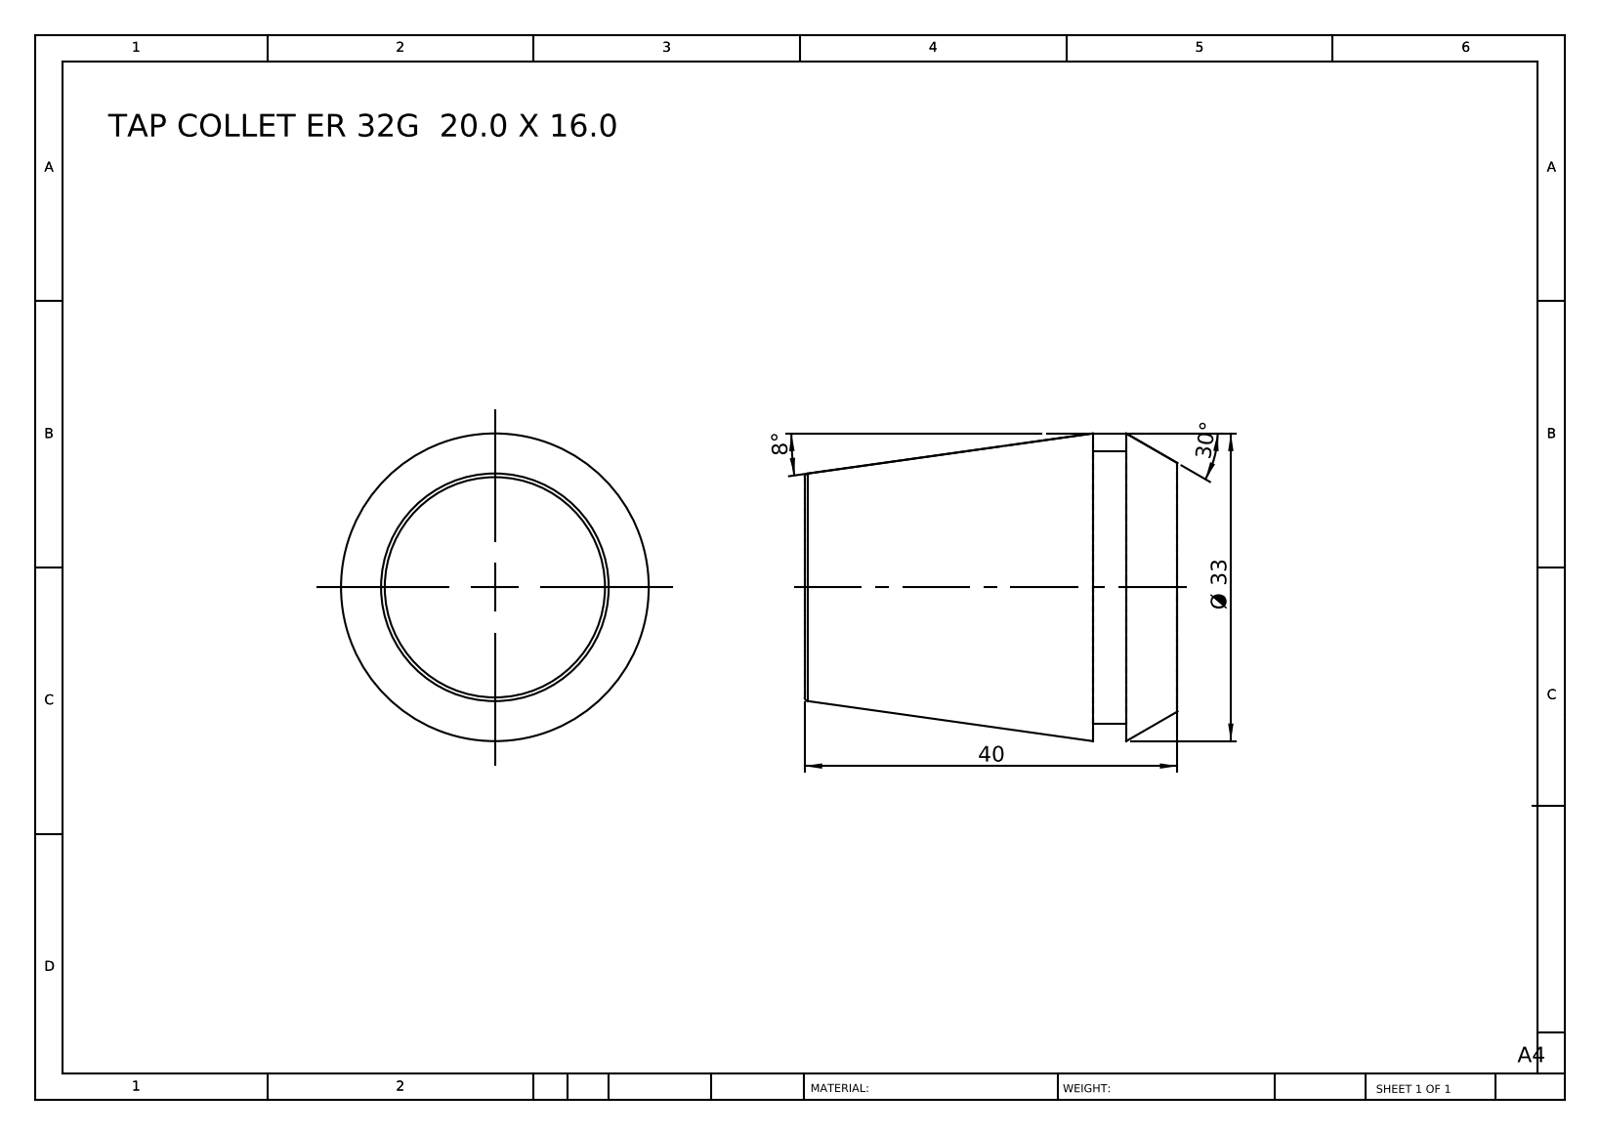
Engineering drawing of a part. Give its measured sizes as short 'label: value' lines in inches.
name: TAP COLLET ER 32G 20.0 X 16.0
written by: SolidWorks 2014 (CONFIG_CONTROL_DESIGN)
unit: in
bodies: 1 solid, 12 faces (4 planar, 2 cylindrical, 6 other)
size: 1.575 × 1.299 × 1.299
volume: 1.608 in³; area: 7.934 in²
bosses: 1× ⌀1.15
face distances: 1.575, 0.358, 1.217, 0.217, 0.142, 1.358
